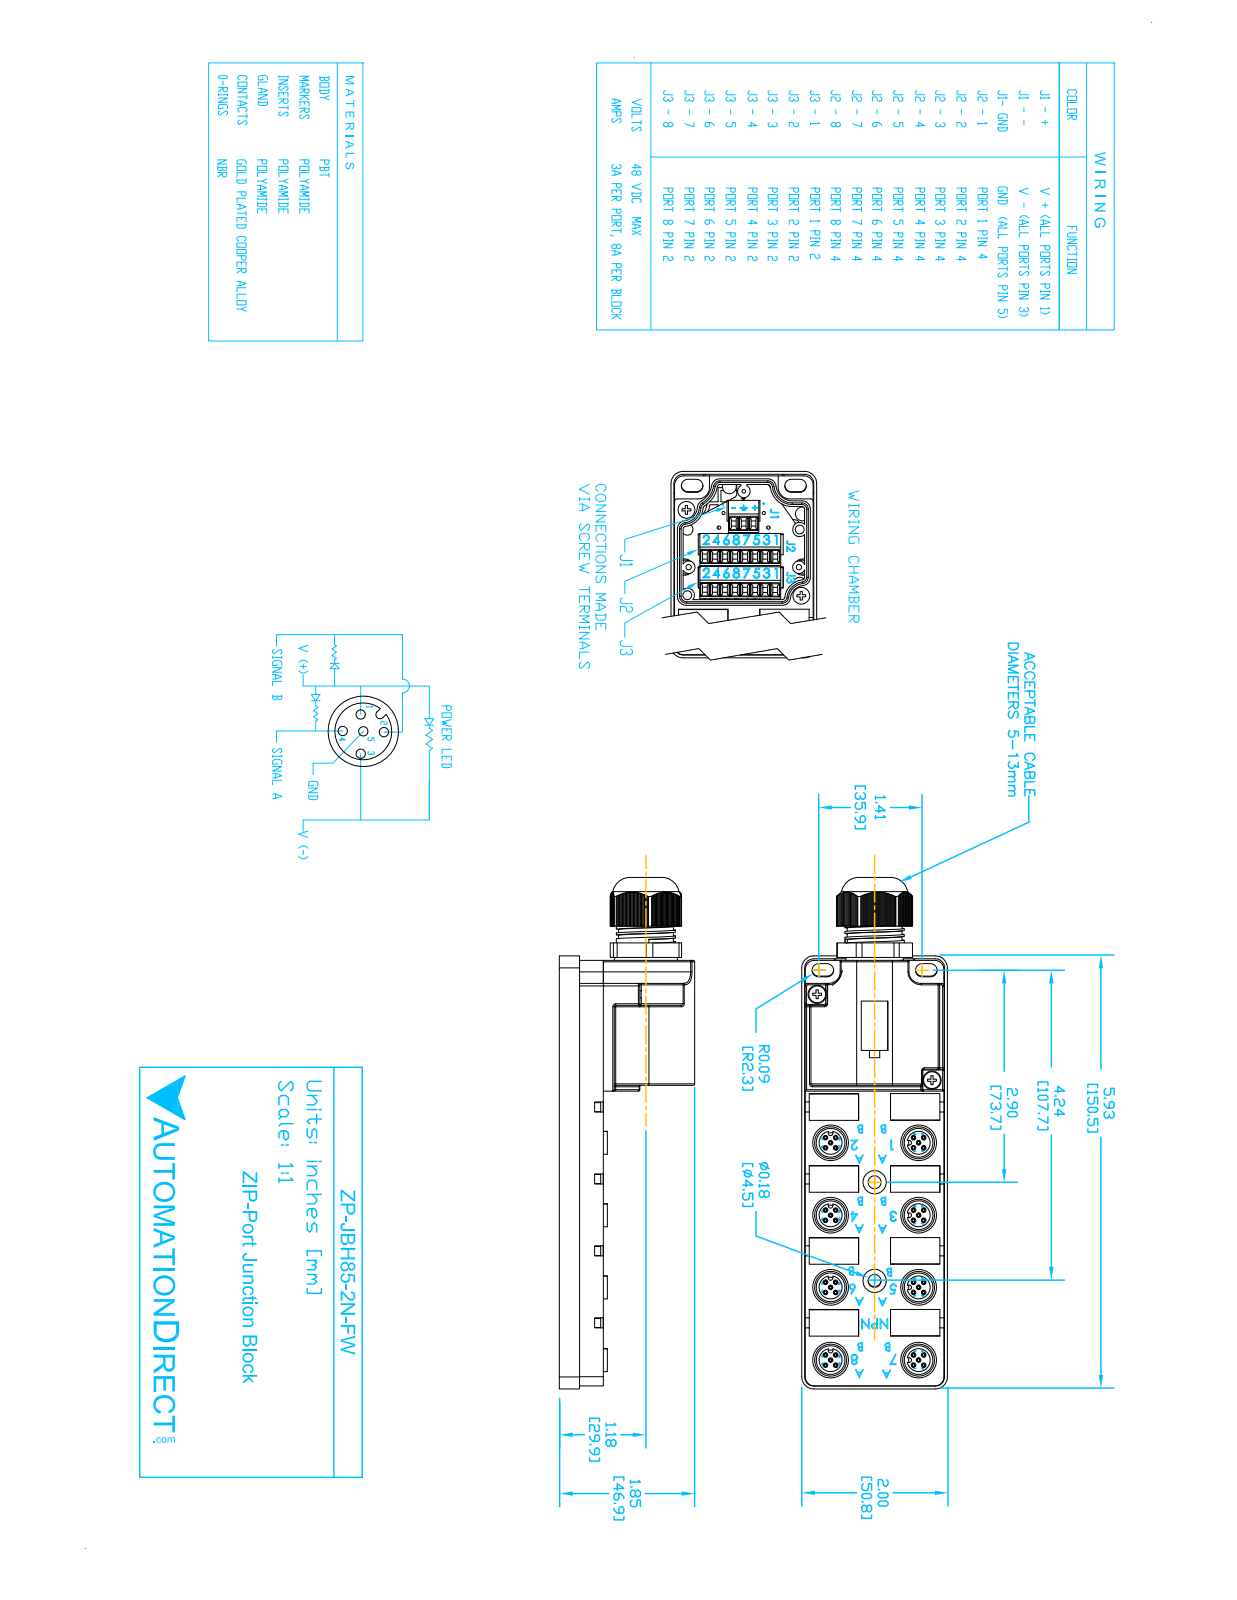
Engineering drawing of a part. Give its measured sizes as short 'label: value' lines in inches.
name: ZP-JBH85-00-FW
written by: SolidWorks 2017 (AUTOMOTIVE_DESIGN)
unit: in
bodies: 10 solids, 1530 faces (862 planar, 393 cylindrical, 275 other)
size: 6.959 × 1.991 × 1.851
volume: 10.28 in³; area: 59.48 in²
holes: 40× ⌀0.043, 40× ⌀0.063, 8× ⌀0.437, 8× ⌀0.488, 2× ⌀0.177, 2× ⌀0.25, 2× ⌀0.26, 2× ⌀0.318, 1× ⌀0.3, 1× ⌀0.37, 1× ⌀0.49, 1× ⌀0.597
bosses: 7× ⌀0.315, 2× ⌀0.23, 1× ⌀0.81, 1× ⌀0.315
rounds: 34× R0.02, 8× R0.031, 4× R0.035, 4× R0.09, 4× R0.164, 2× R0.126, 2× R0.156, 2× R0.625
face distances: 0.6, 0.035, 0.035, 0.031, 0.6, 0.565, 1.896, 0.596, 1.944, 0.048
hole spacings: 0.098, 0.139, 1.204, 1.136, 1.275, 0.991, 1.559, 0.197
